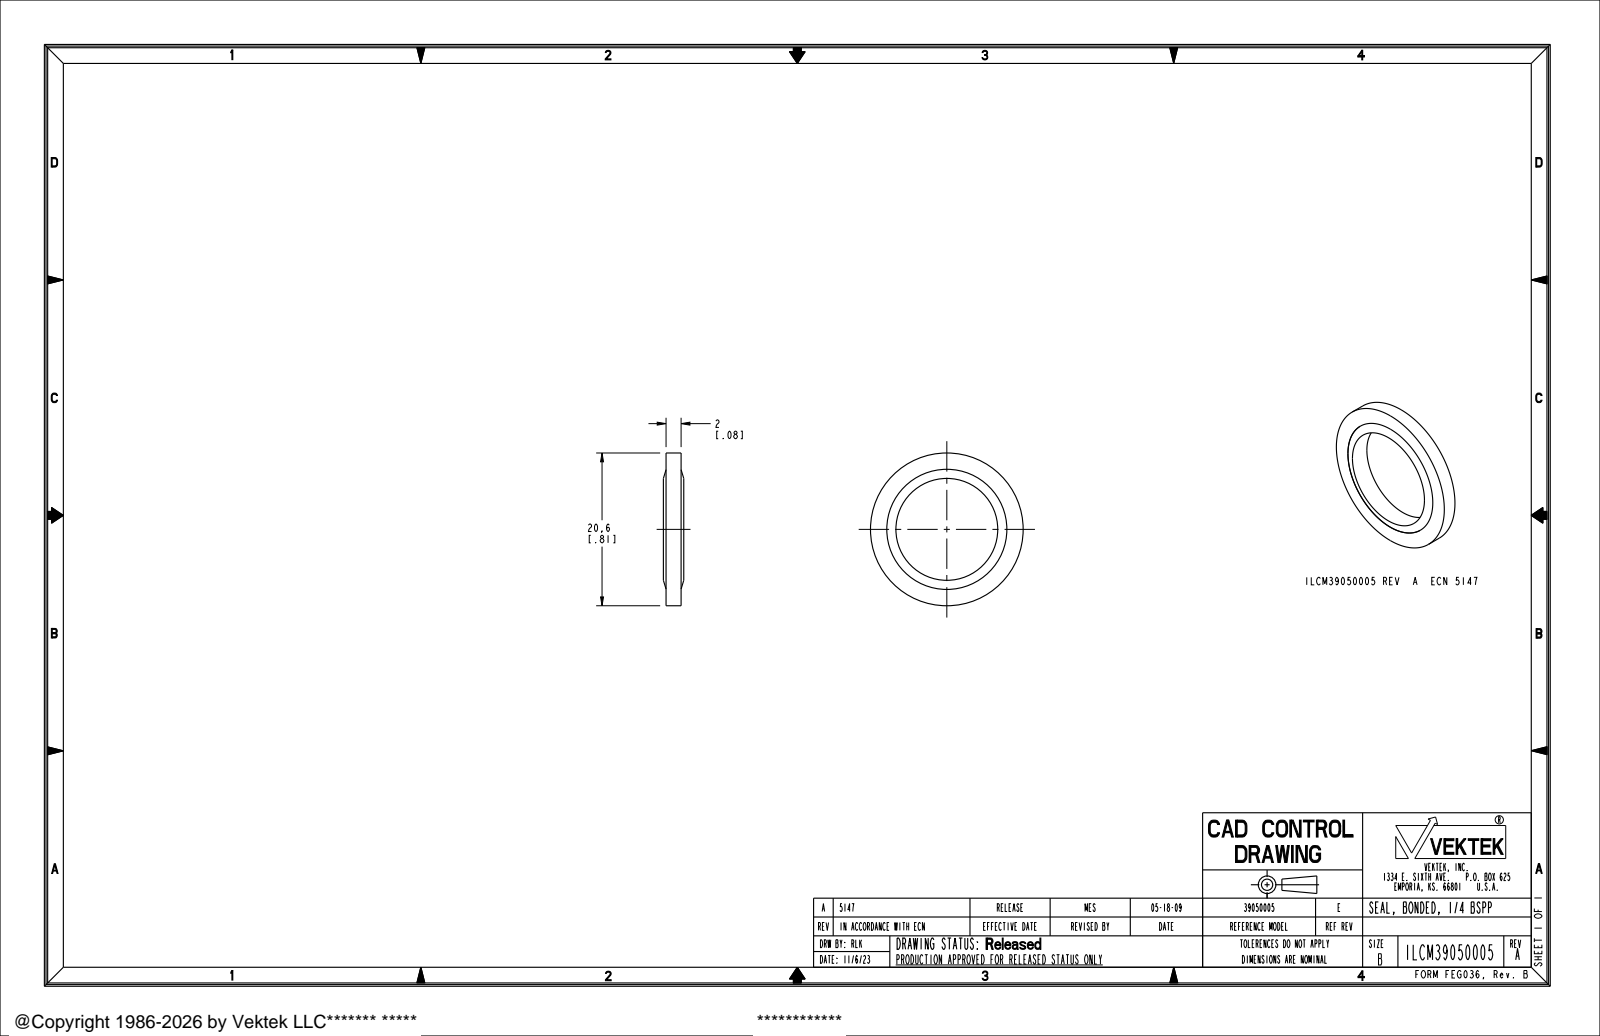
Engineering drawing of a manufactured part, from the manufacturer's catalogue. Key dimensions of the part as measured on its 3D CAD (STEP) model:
Part name (STEP PRODUCT): ILCM39050005RING; ILCM39050005SEAL; ILCM39050005
STEP written by: CREO PARAMETRIC BY PTC INC, 2021164 (AUTOMOTIVE_DESIGN)
Units: inches
Bodies: 2 solids, 14 faces (2 planar, 8 cylindrical, 4 other)
Overall size (bounding box): 0.811 × 0.811 × 0.108
Volume: 0.024 in³ · Surface area: 1.287 in²
Round holes (diameter × count): ⌀0.541 ×1, ⌀0.638 ×1
Round bosses / shafts (diameter × count): ⌀0.811 ×1
Main face-to-face distances: 0.08
